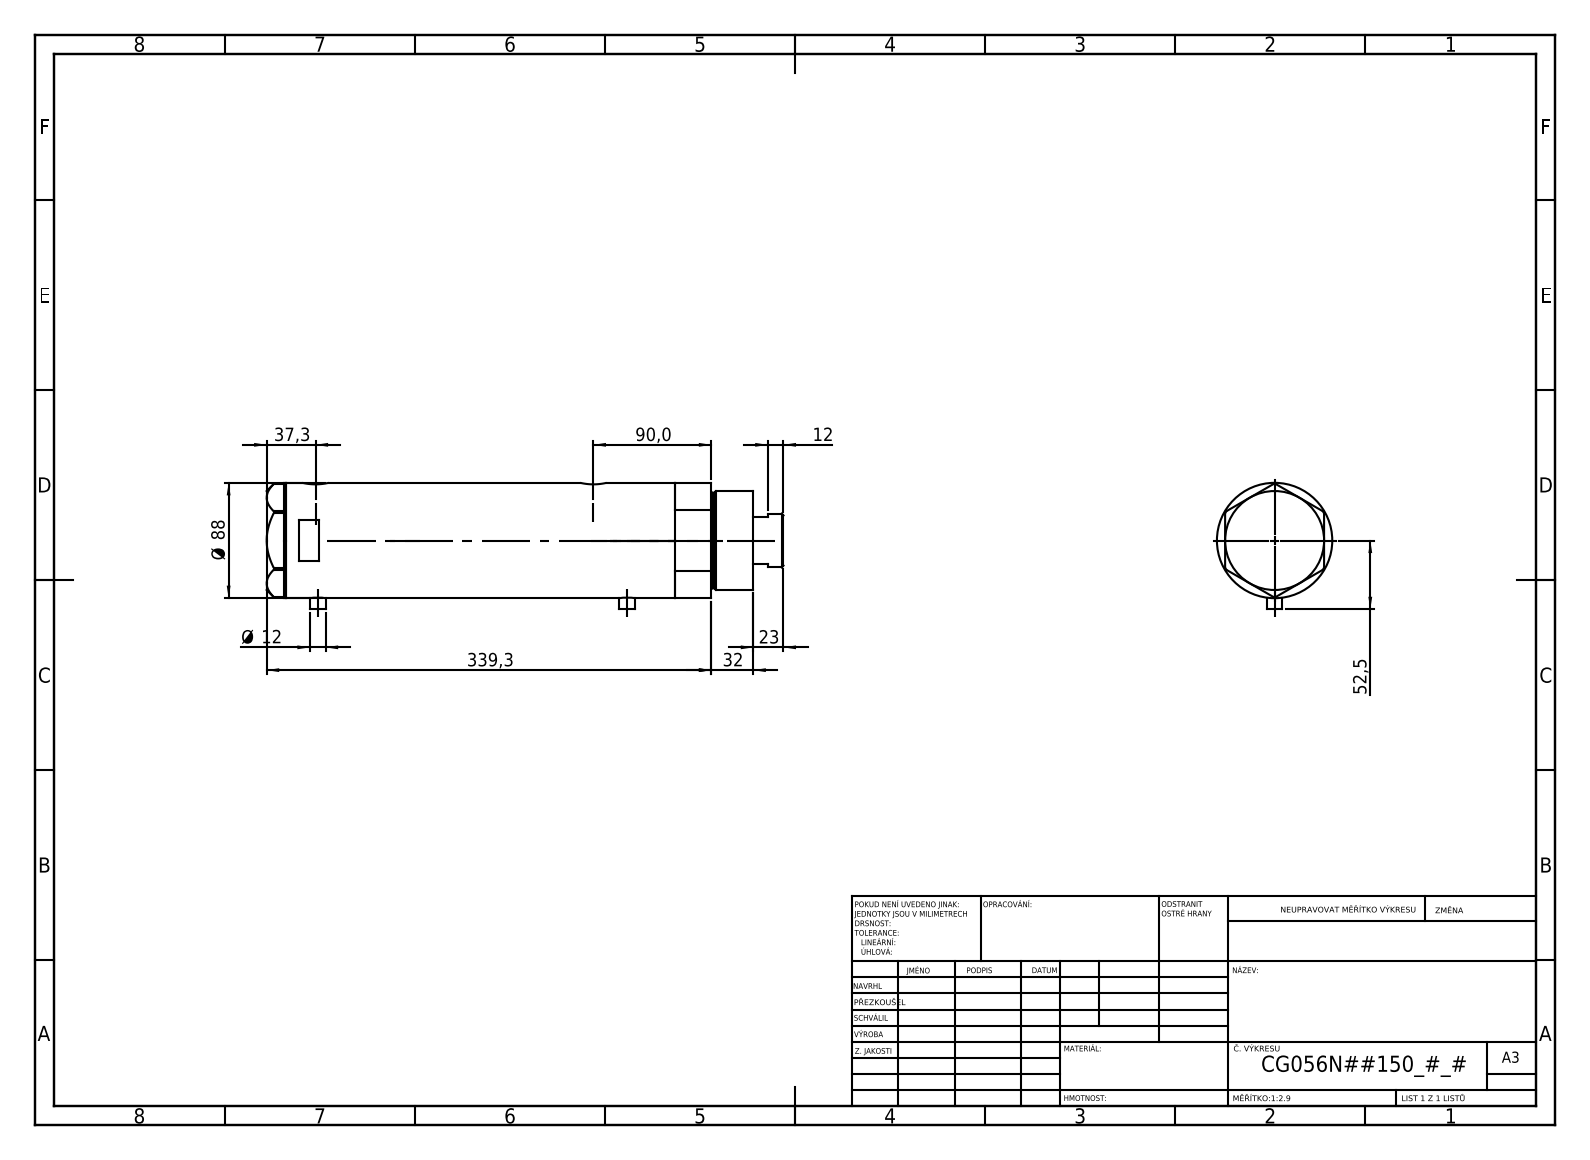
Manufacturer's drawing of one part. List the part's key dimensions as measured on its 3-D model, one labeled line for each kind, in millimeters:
Part name (STEP PRODUCT): V270CG_BACK; V270CG_FRONT; V270CG_VC; V270CG_MIDDLE
STEP written by: SolidWorks 2019 (CONFIG_CONTROL_DESIGN)
Units: millimetres
Bodies: 4 solids, 121 faces (52 planar, 49 cylindrical, 20 other)
Overall size (bounding box): 394.3 × 96.5 × 88
Volume: 2 034 000 mm³ · Surface area: 279 868 mm²
Round holes (diameter × count): ⌀12.5 ×2, ⌀13.16 ×2, ⌀20 ×2, ⌀14.5 ×1, ⌀42 ×1, ⌀43.5 ×1, ⌀56 ×1, ⌀60 ×1, ⌀80 ×1
Round bosses / shafts (diameter × count): ⌀12 ×2, ⌀88 ×1, ⌀75 ×1, ⌀73 ×1, ⌀41 ×1
Main face-to-face distances: 234.4, 26, 208.4, 15, 41, 249.4, 356.3, 371.3, 330.3, 121.9
Hole centre spacings: 1.7, 25.8, 210.3, 212, 236.1, 237.8
